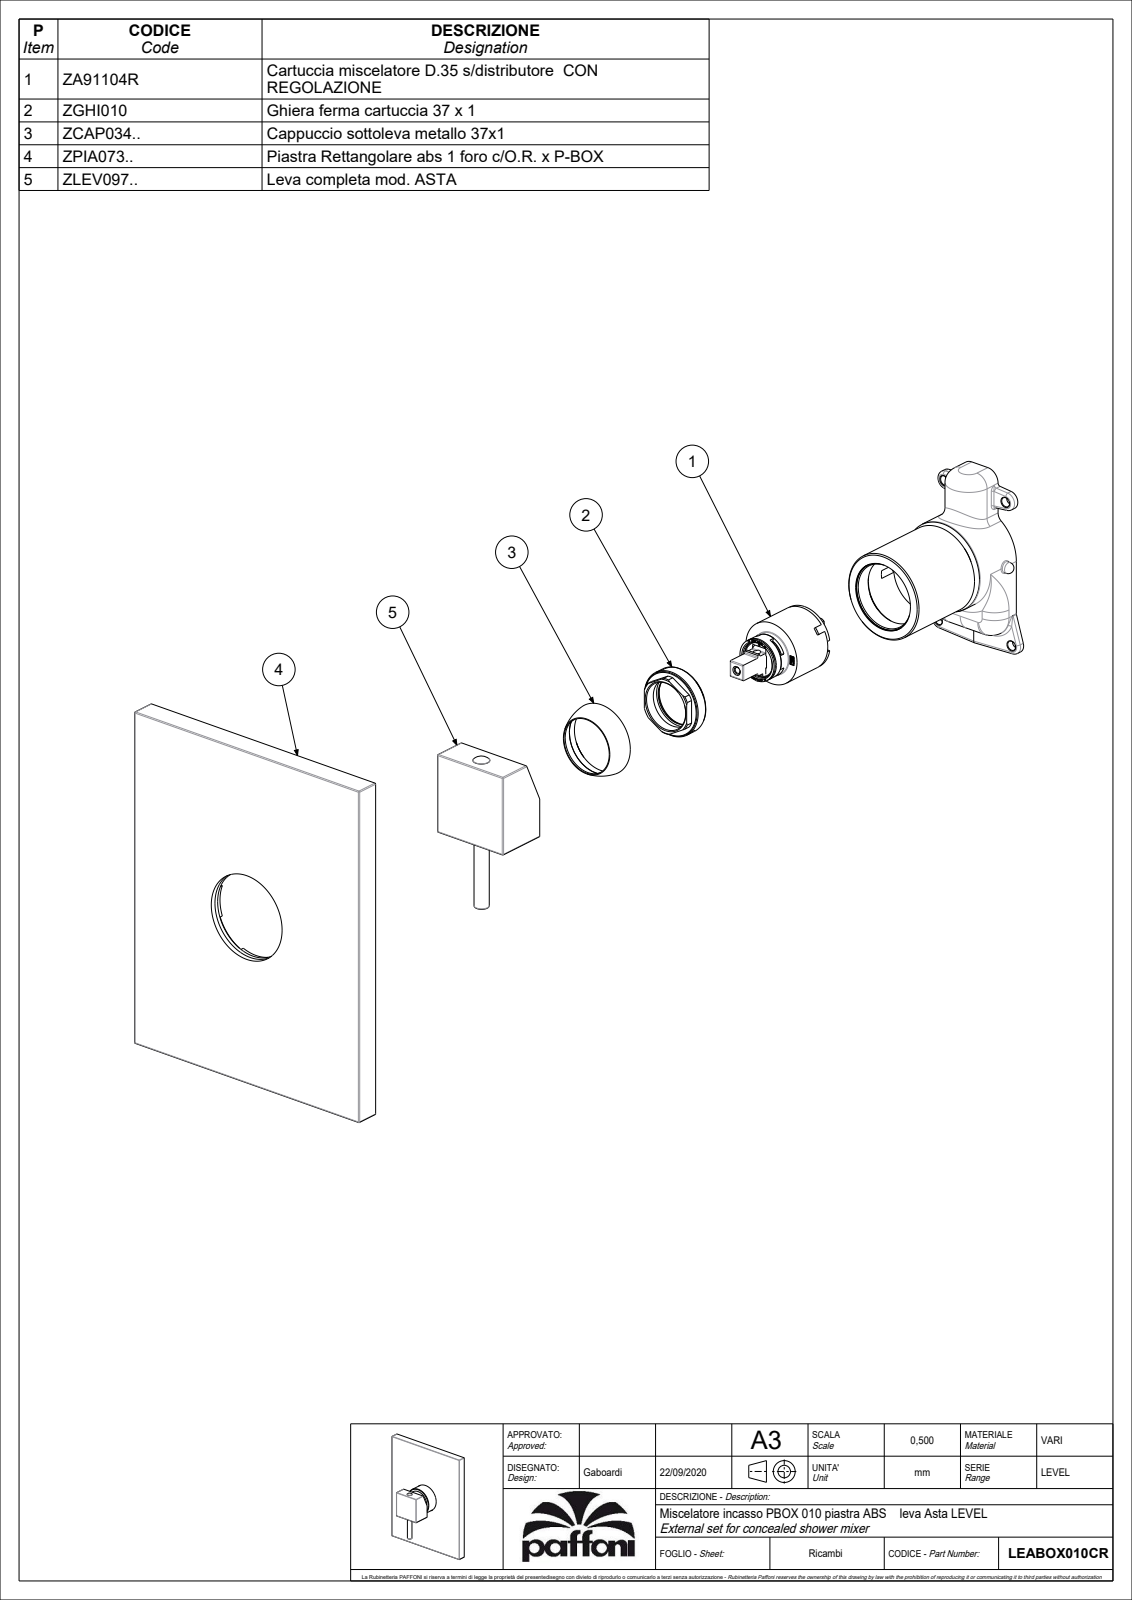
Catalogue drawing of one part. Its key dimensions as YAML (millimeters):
part_name: "LEABOX010CR"
step_written_by: "CREO PARAMETRIC BY PTC INC, 2020044 (CONFIG_CONTROL_DESIGN)"
units: millimeters
bodies: {solids: 2, faces: 1039, planar: 650, cylindrical: 247, other: 142}
overall_size: [192, 154, 66.1]
volume: 295628
surface_area: 120778
round_holes:
  - {diameter: 5, count: 3}
  - {diameter: 7, count: 3}
  - {diameter: 2, count: 2}
  - {diameter: 4, count: 2}
  - {diameter: 3.3, count: 1}
  - {diameter: 5.5, count: 1}
  - {diameter: 6, count: 1}
  - {diameter: 8.1, count: 1}
  - {diameter: 19.5, count: 1}
  - {diameter: 19.9, count: 1}
  - {diameter: 26.8, count: 1}
  - {diameter: 29, count: 1}
round_bosses_or_shafts:
  - {diameter: 4.8, count: 2}
  - {diameter: 57, count: 1}
  - {diameter: 48.1, count: 1}
  - {diameter: 39, count: 1}
  - {diameter: 35, count: 1}
  - {diameter: 34.8, count: 1}
  - {diameter: 32.2, count: 1}
  - {diameter: 23.5, count: 1}
partial_cylinders:
  - {radius: 0.5, count: 45}
  - {radius: 0.15, count: 11}
  - {radius: 0.3, count: 4}
  - {radius: 1, count: 2}
  - {radius: 2.5, count: 1}
  - {radius: 7, count: 1}
  - {radius: 9.3, count: 1}
  - {radius: 10.85, count: 1}
face_to_face_distances: [13.5, 3, 10.5, 23.5, 52.6, 130.5, 31, 154, 99.5, 54.5]
hole_center_spacings: [8.6, 13.45, 15.13, 21.93, 14, 14.6, 18]
